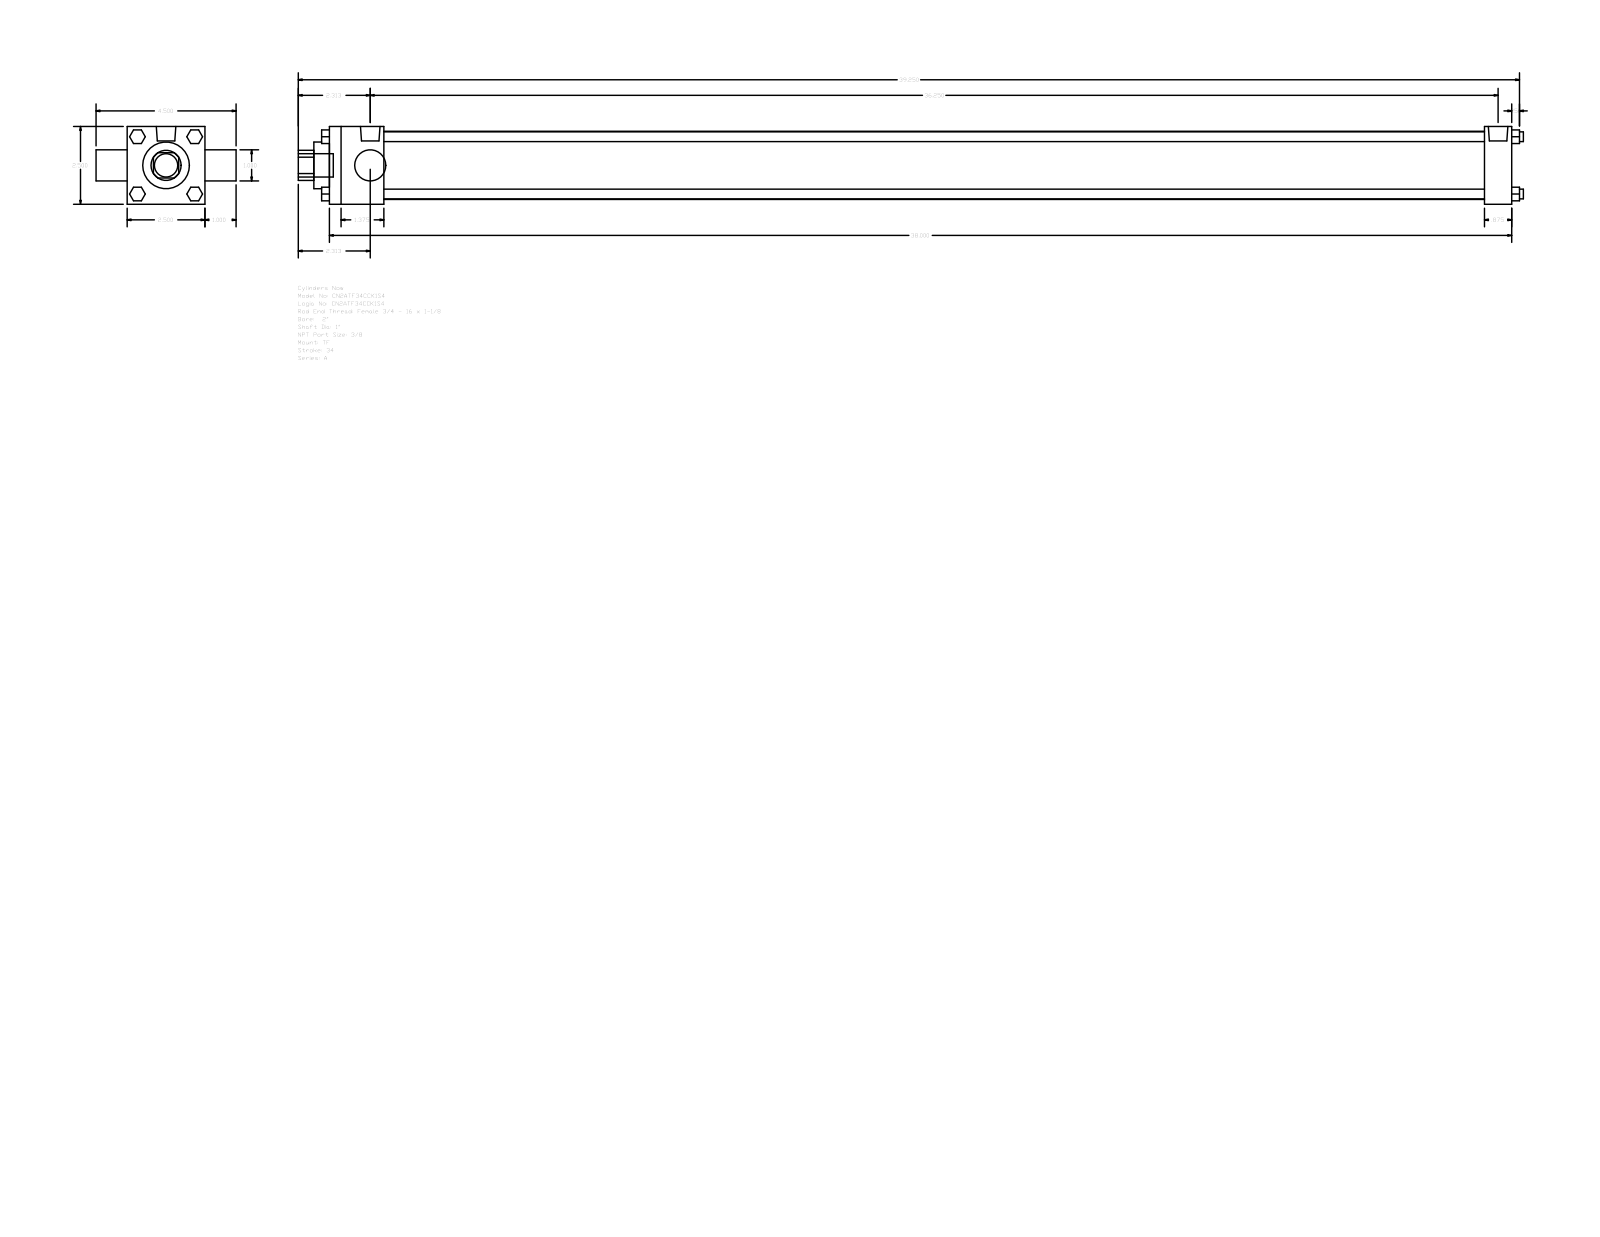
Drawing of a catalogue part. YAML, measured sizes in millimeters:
part_name: "A_TF__0200_1"
step_written_by: "GSSL Pune (CONFIG_CONTROL_DESIGN)"
units: millimeters
bodies: {solids: 0, faces: 120, planar: 92, cylindrical: 28, other: 0}
overall_size: [1000.12, 114.3, 63.5]
round_holes:
  - {diameter: 25.4, count: 2}
  - {diameter: 38.1, count: 1}
  - {diameter: 55.63, count: 1}
round_bosses_or_shafts:
  - {diameter: 7.94, count: 4}
  - {diameter: 5.56, count: 3}
  - {diameter: 15.93, count: 2}
  - {diameter: 19.05, count: 1}
partial_cylinders:
  - {radius: 12.29, count: 1}
face_to_face_distances: [63.5, 965.2, 44.45, 942.98, 898.53, 920.75, 22.22, 25.4, 88.9, 977.9]
